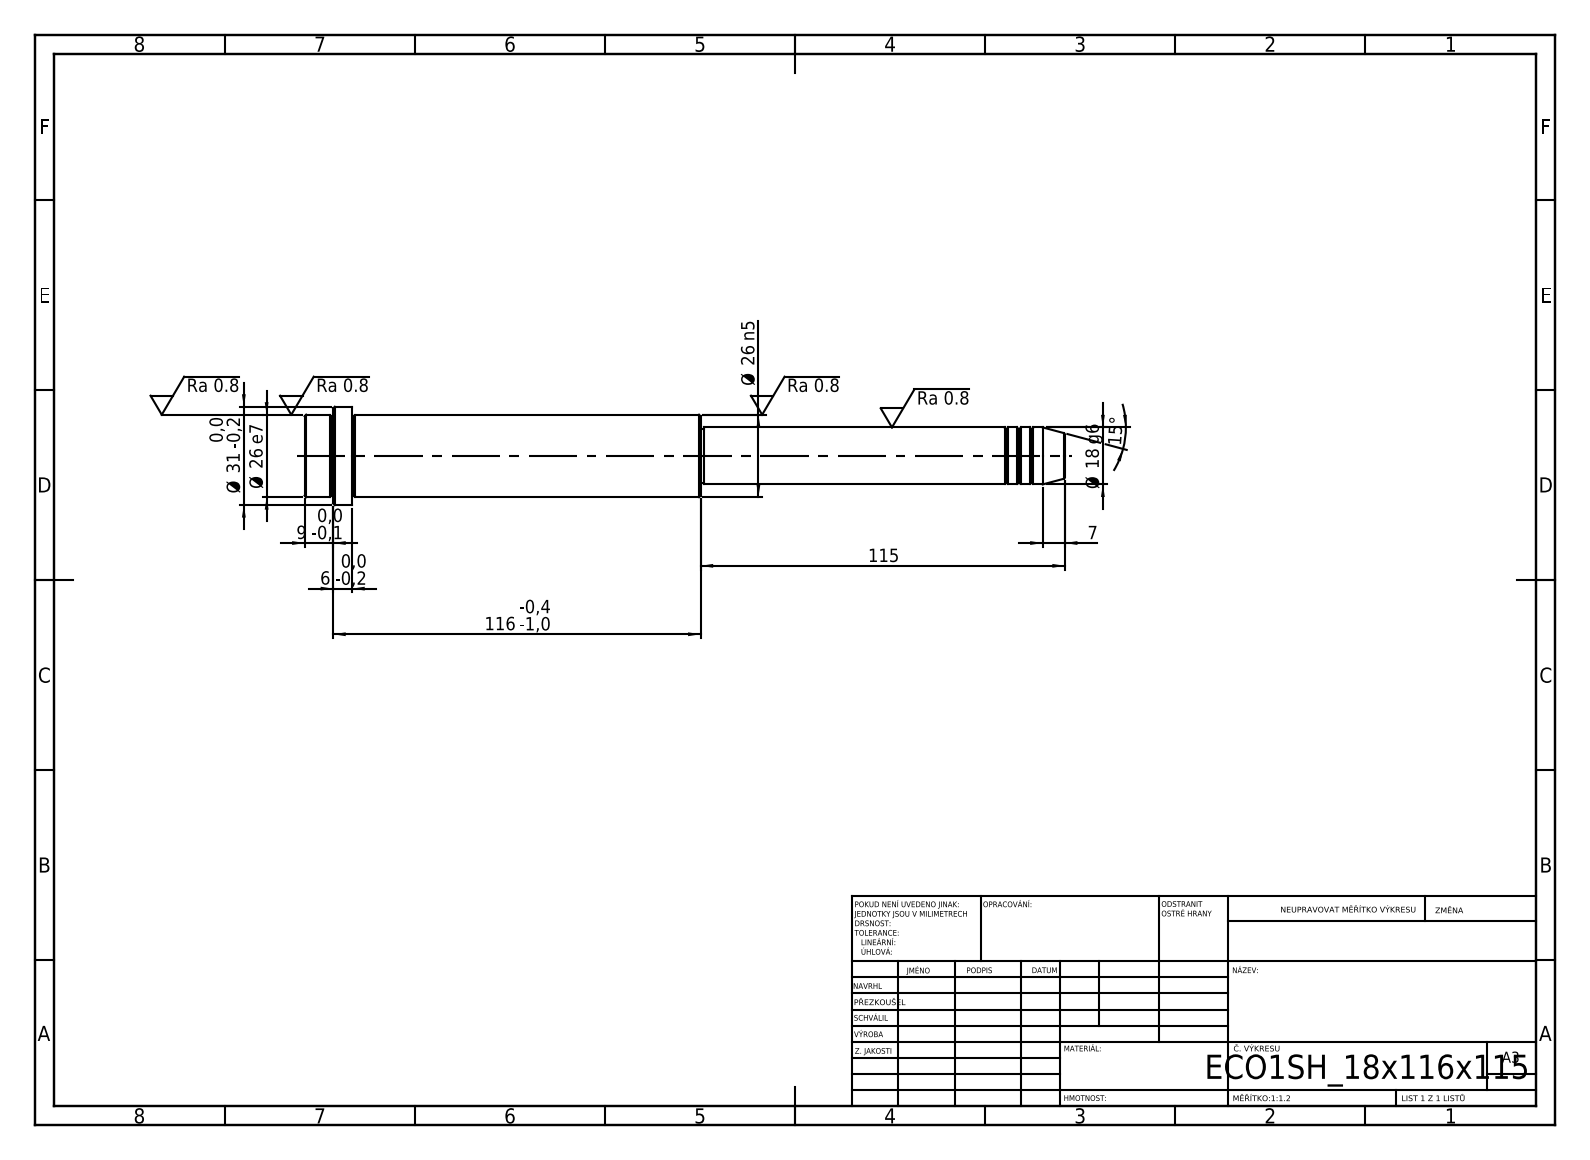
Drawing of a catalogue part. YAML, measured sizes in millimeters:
step_written_by: "SolidWorks 2019 (CONFIG_CONTROL_DESIGN)"
units: millimeters
bodies: {solids: 1, faces: 52, planar: 6, cylindrical: 16, other: 30}
overall_size: [240, 31, 31]
volume: 96439
surface_area: 18337
round_bosses_or_shafts:
  - {diameter: 31, count: 1}
  - {diameter: 26, count: 1}
  - {diameter: 18, count: 1}
  - {diameter: 17, count: 1}
face_to_face_distances: [125, 110, 15, 116, 6, 9, 115, 225, 231, 240]
